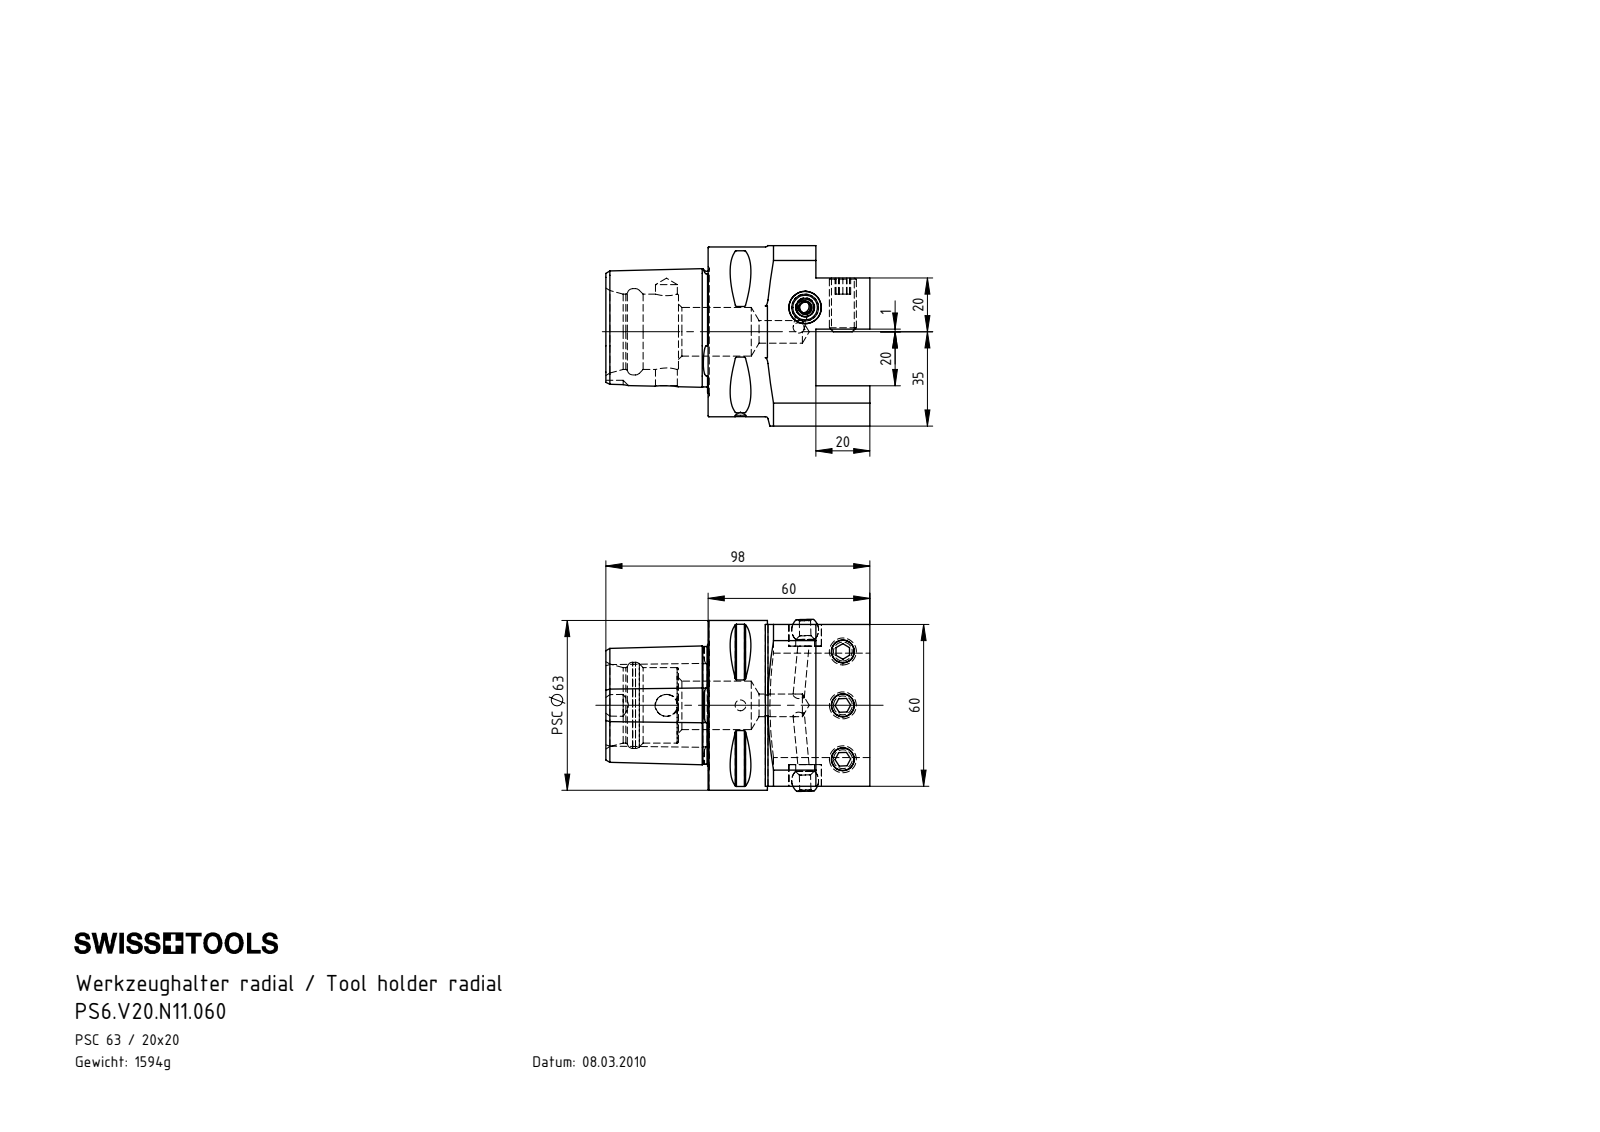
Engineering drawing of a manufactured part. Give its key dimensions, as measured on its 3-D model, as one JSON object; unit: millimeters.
{"part_name": "KU1-U12.001.010_1; KU1-U12.001.010; PS6-V20.N11.060; ISO 4026 - M10 x 20_PreviewCfg (+2 more)", "step_written_by": "SolidWorks 2012 (CONFIG_CONTROL_DESIGN)", "units": "millimeters", "bodies": {"solids": 8, "faces": 243, "planar": 66, "cylindrical": 69, "other": 108}, "overall_size": [98, 67, 64.38], "volume_mm3": 203706, "surface_area_mm2": 38862, "round_holes": [[4.2, 4], [8.5, 3], [4, 1], [7, 1], [8.1, 1], [8.4, 1], [12, 1], [18, 1], [28, 1], [32, 1]], "round_bosses_or_shafts": [[10, 3], [63, 1]], "partial_cylinders_radius": [[0.5, 8], [6, 1], [40, 1]], "face_to_face_distances": [60, 40, 20, 15, 52, 55, 36, 21, 19, 67], "hole_center_spacings": [20, 42.94, 68.49, 27.5, 38, 40, 65.5]}
